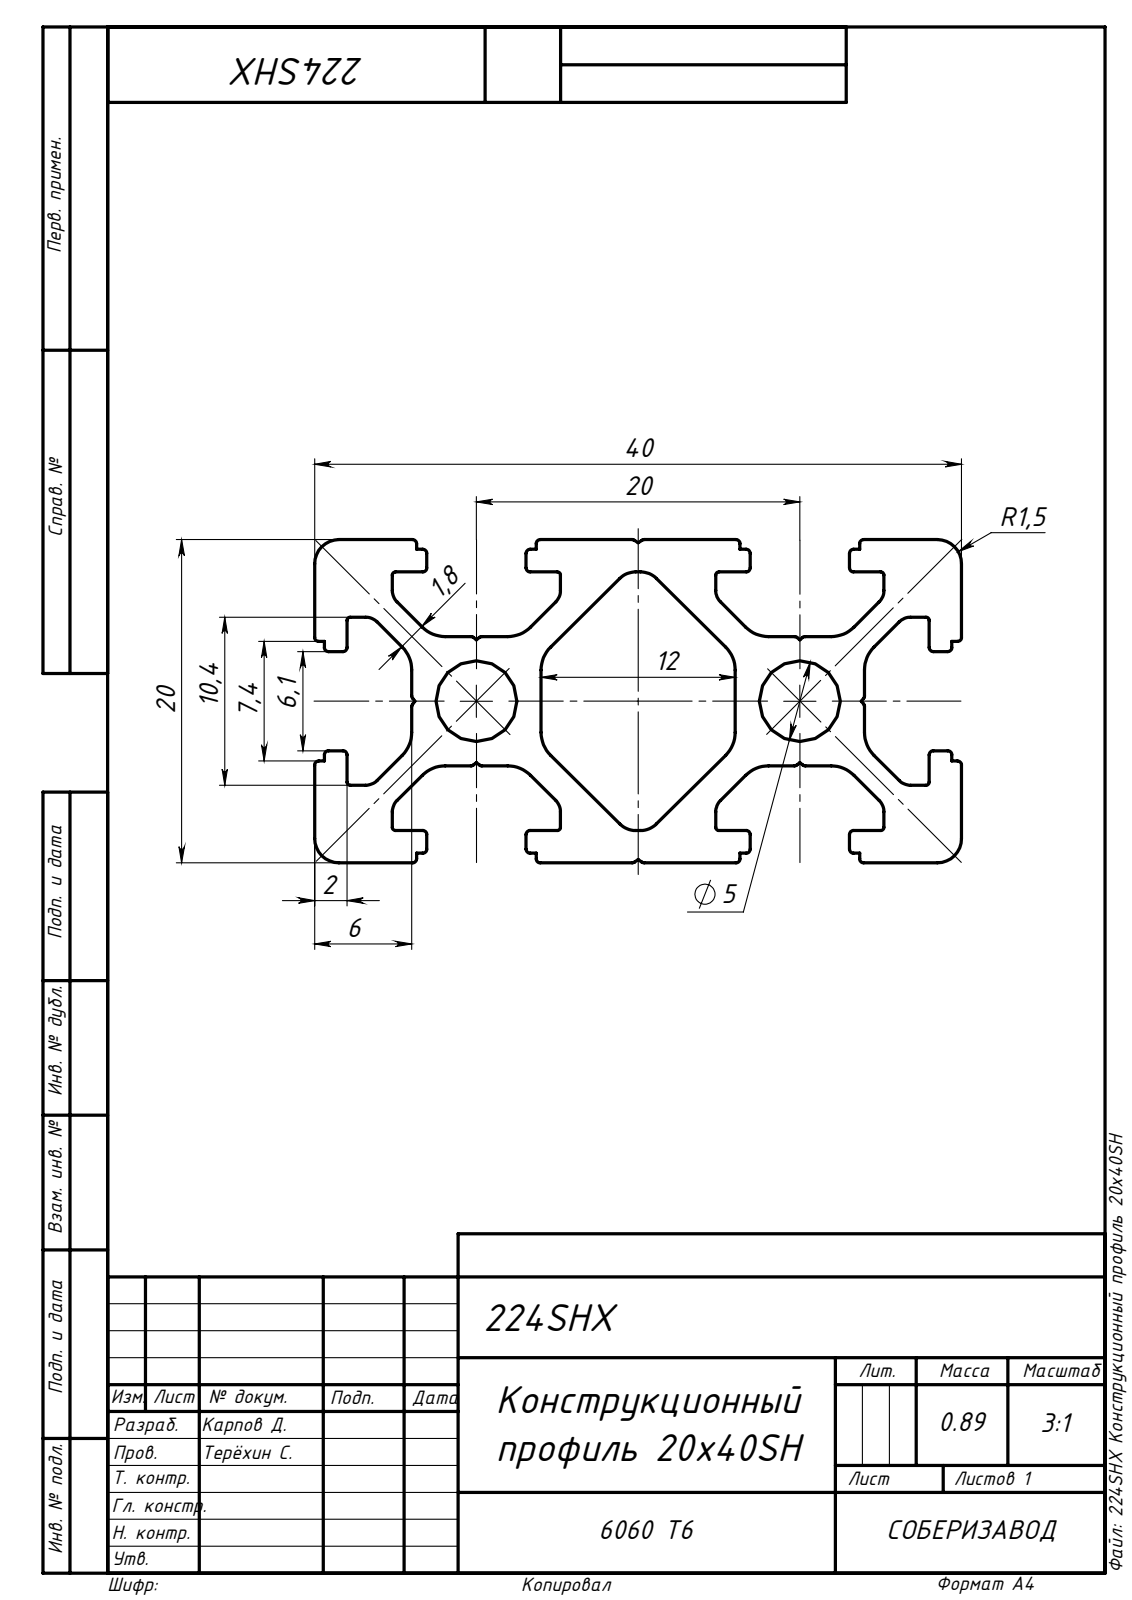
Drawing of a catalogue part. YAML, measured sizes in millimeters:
step_written_by: "SolidWorks 2019 (AUTOMOTIVE_DESIGN)"
units: millimeters
bodies: {solids: 1, faces: 226, planar: 122, cylindrical: 104, other: 0}
overall_size: [1000, 40, 20]
volume: 330855
surface_area: 293133
round_holes:
  - {diameter: 5, count: 2}
partial_cylinders:
  - {radius: 0.25, count: 52}
  - {radius: 2, count: 16}
  - {radius: 0.2, count: 12}
  - {radius: 1, count: 12}
  - {radius: 1.4, count: 4}
  - {radius: 1.5, count: 4}
face_to_face_distances: [20, 12, 2, 14, 6, 4, 18, 8, 12.36, 1.2]
hole_center_spacings: [20]
